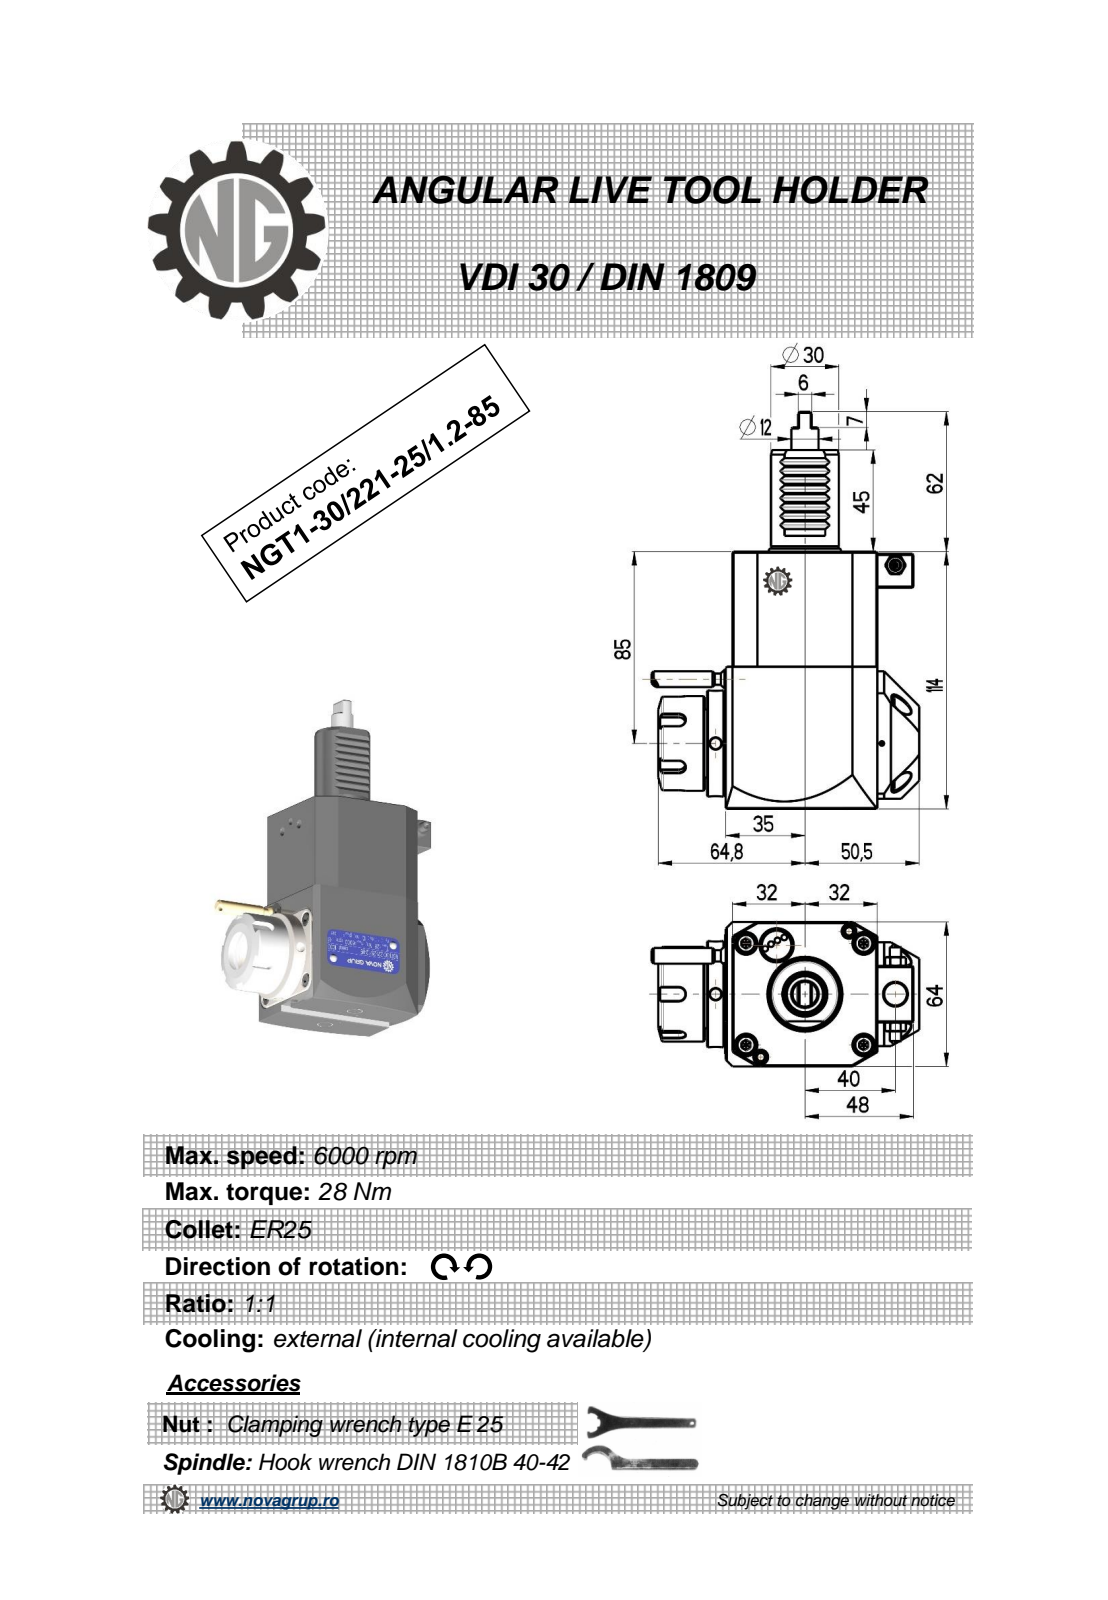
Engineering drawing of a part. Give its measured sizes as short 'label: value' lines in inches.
name: NGT1_30_221_25_1_2_85
written by: PRO/ENGINEER BY PARAMETRIC TECHNOLOGY CORPORATION, 2010280 (CONFIG_CONTROL_DESIGN)
unit: in
bodies: 1 solid, 409 faces (183 planar, 84 cylindrical, 142 other)
size: 6.929 × 4.56 × 2.52
volume: 34.58 in³; area: 82.42 in²
holes: 2× ⌀0.197, 1× ⌀0.098, 1× ⌀0.118, 1× ⌀0.165, 1× ⌀0.374, 1× ⌀0.394, 1× ⌀0.799
bosses: 2× ⌀0.353, 2× ⌀0.197, 1× ⌀1.85, 1× ⌀1.654, 1× ⌀1.433, 1× ⌀1.299, 1× ⌀1.181, 1× ⌀0.472
rounds: 12× R0.01, 8× R0.012, 5× R0.118, 2× R0.031, 2× R6.299, 1× R1.26
face distances: 2.52, 4.488, 3.009, 0.126, 2.646, 2.638, 0.02, 0.118, 0.315, 0.295
hole spacings: 1.307, 2.005, 3.012, 3.128, 4.411
